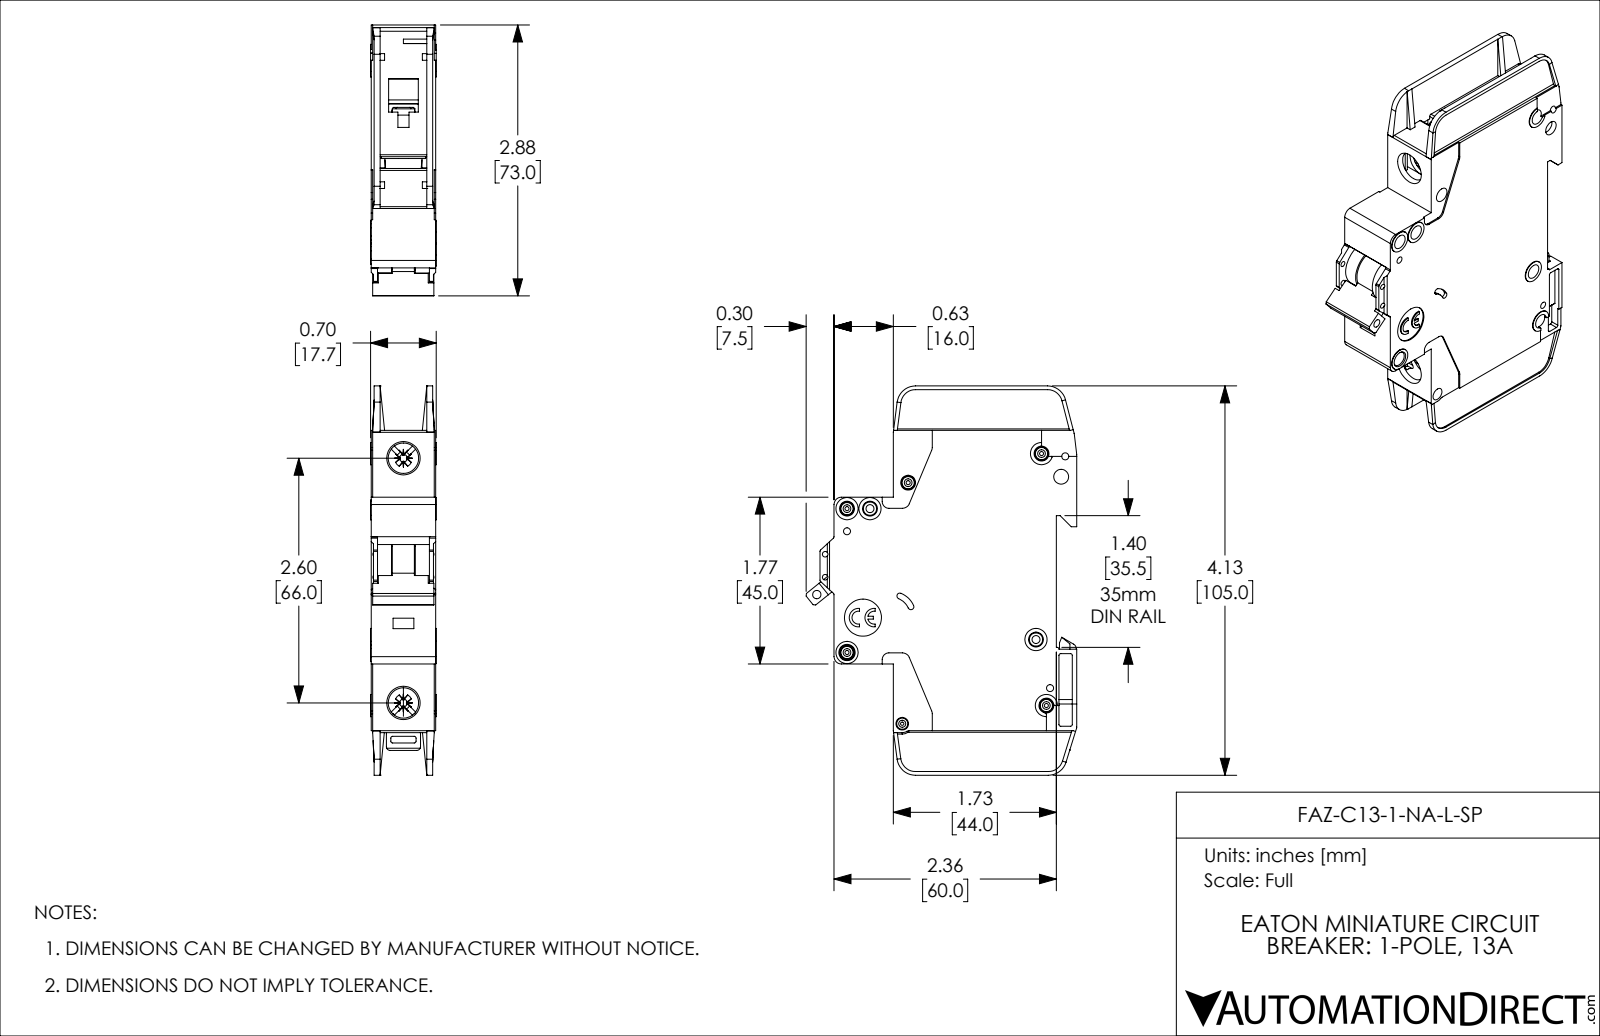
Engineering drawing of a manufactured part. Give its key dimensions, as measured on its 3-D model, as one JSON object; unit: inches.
{"part_name": "FAZ-C13-1-NA-L-SP", "step_written_by": "SolidWorks 2019 (AUTOMOTIVE_DESIGN)", "units": "inches", "bodies": {"solids": 1, "faces": 1127, "planar": 671, "cylindrical": 357, "other": 99}, "overall_size": [4.134, 2.876, 0.697], "volume_in3": 4.682, "surface_area_in2": 41.01, "round_holes": [[0.157, 8], [0.043, 5], [0.075, 4], [0.059, 2], [0.085, 2], [0.323, 2], [0.035, 1], [0.089, 1], [0.098, 1], [0.134, 1], [0.394, 1]], "round_bosses_or_shafts": [[0.13, 5], [0.236, 4], [0.118, 2], [0.098, 1]], "partial_cylinders_radius": [[0.02, 42], [0.016, 10], [0.039, 10], [0.079, 8], [0.197, 5], [0.008, 4], [0.026, 4], [0.043, 4]], "face_to_face_distances": [0.047, 0.685, 0.591, 0.638, 0.094, 0.543, 0.016, 0.031, 0.496, 0.575], "hole_center_spacings": [0.244, 0.537, 0.87, 0.189, 0.199, 0.204, 0.221, 0.24]}
